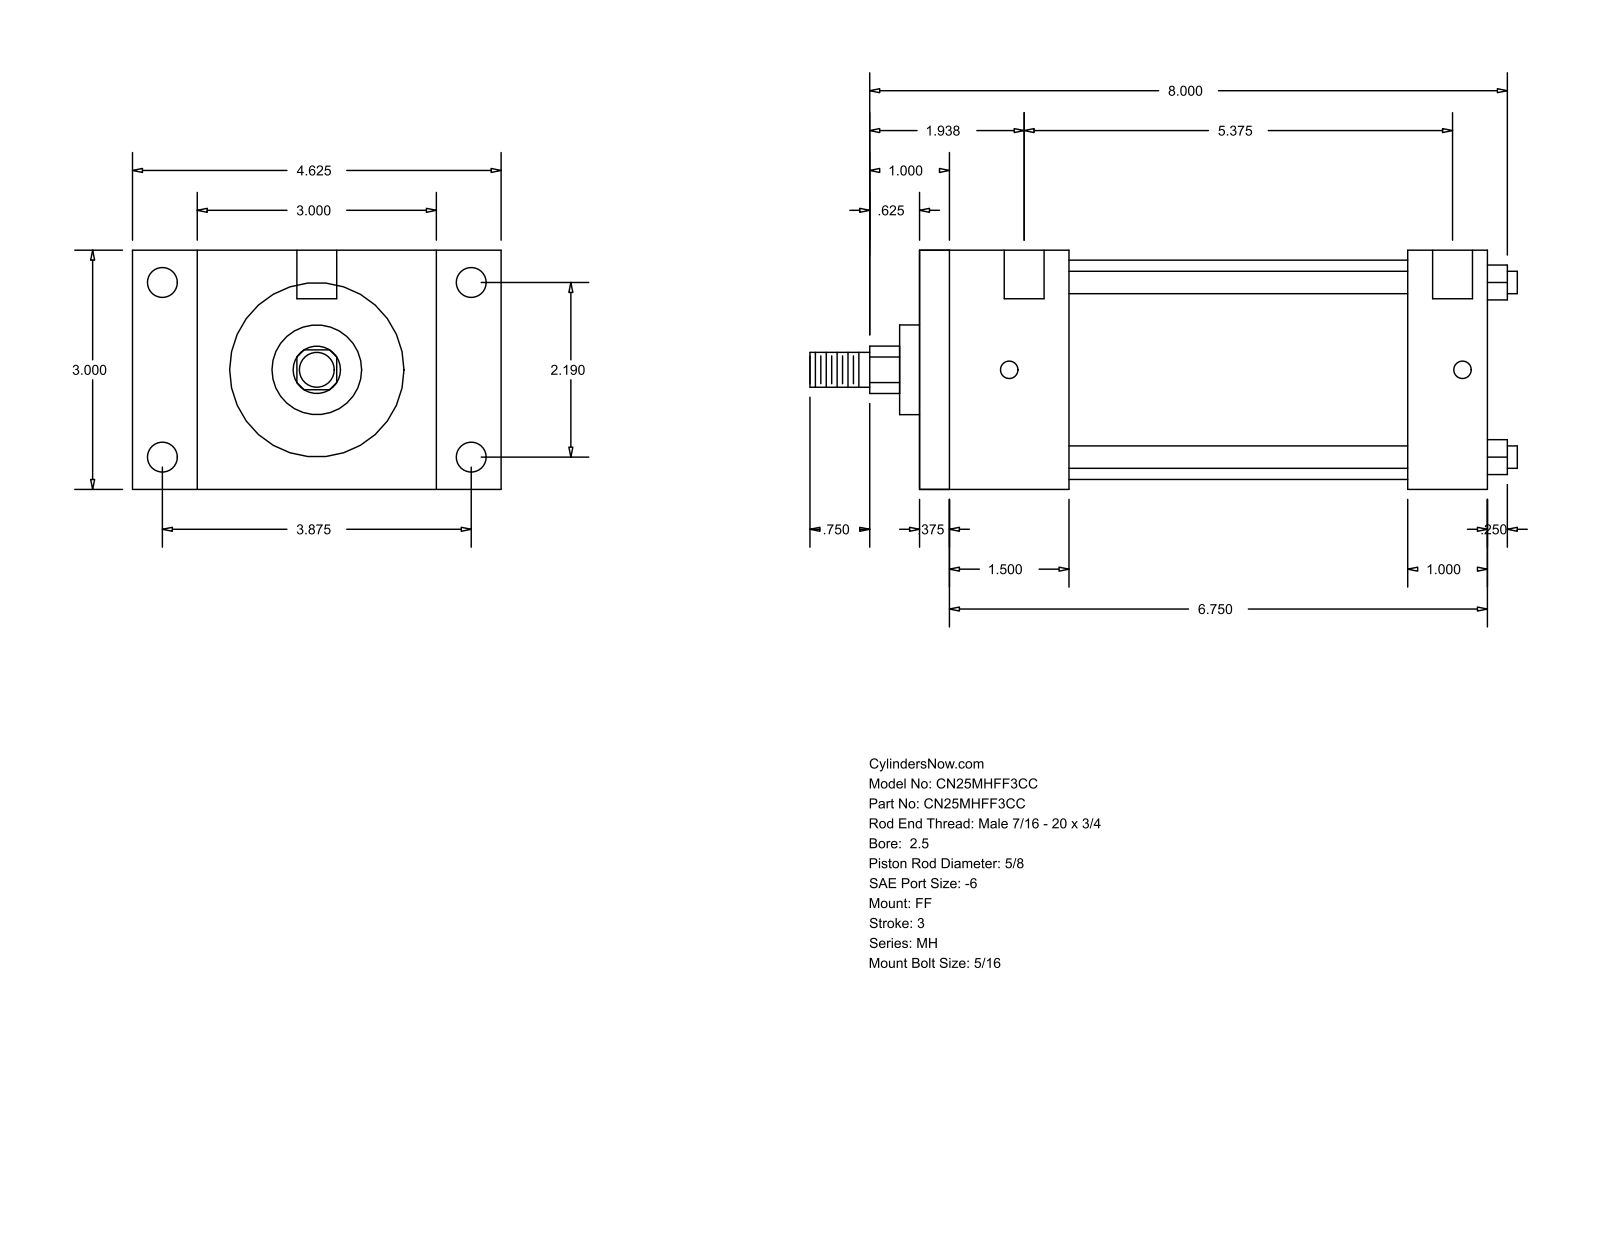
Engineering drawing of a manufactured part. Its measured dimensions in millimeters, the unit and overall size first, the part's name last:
Units: millimetres
Overall size (bounding box): 225.43 × 117.47 × 76.2
Round holes (diameter × count): ⌀5.56 ×4, ⌀9.53 ×4, ⌀12.7 ×2
Round bosses / shafts (diameter × count): ⌀7.14 ×4, ⌀69.85 ×1, ⌀28.57 ×1, ⌀15.88 ×1, ⌀11.11 ×1
Partial cylindrical surfaces — rounded edges, fillets, slot ends (radius × count): R7.54 ×1
Main face-to-face distances: 76.2, 180.97, 171.45, 9.52, 25.4, 47.62, 155.57, 38.1, 146.05, 107.95
Hole centre spacings: 55.62, 98.42, 113.05, 144.46, 3.17, 4.76, 136.53, 139.7
Bodies: 0 solids, 92 faces (64 planar, 28 cylindrical, 0 other)
Part name (STEP PRODUCT): MH_FF__0250_0.625
STEP written by: GSSL Pune (CONFIG_CONTROL_DESIGN)
